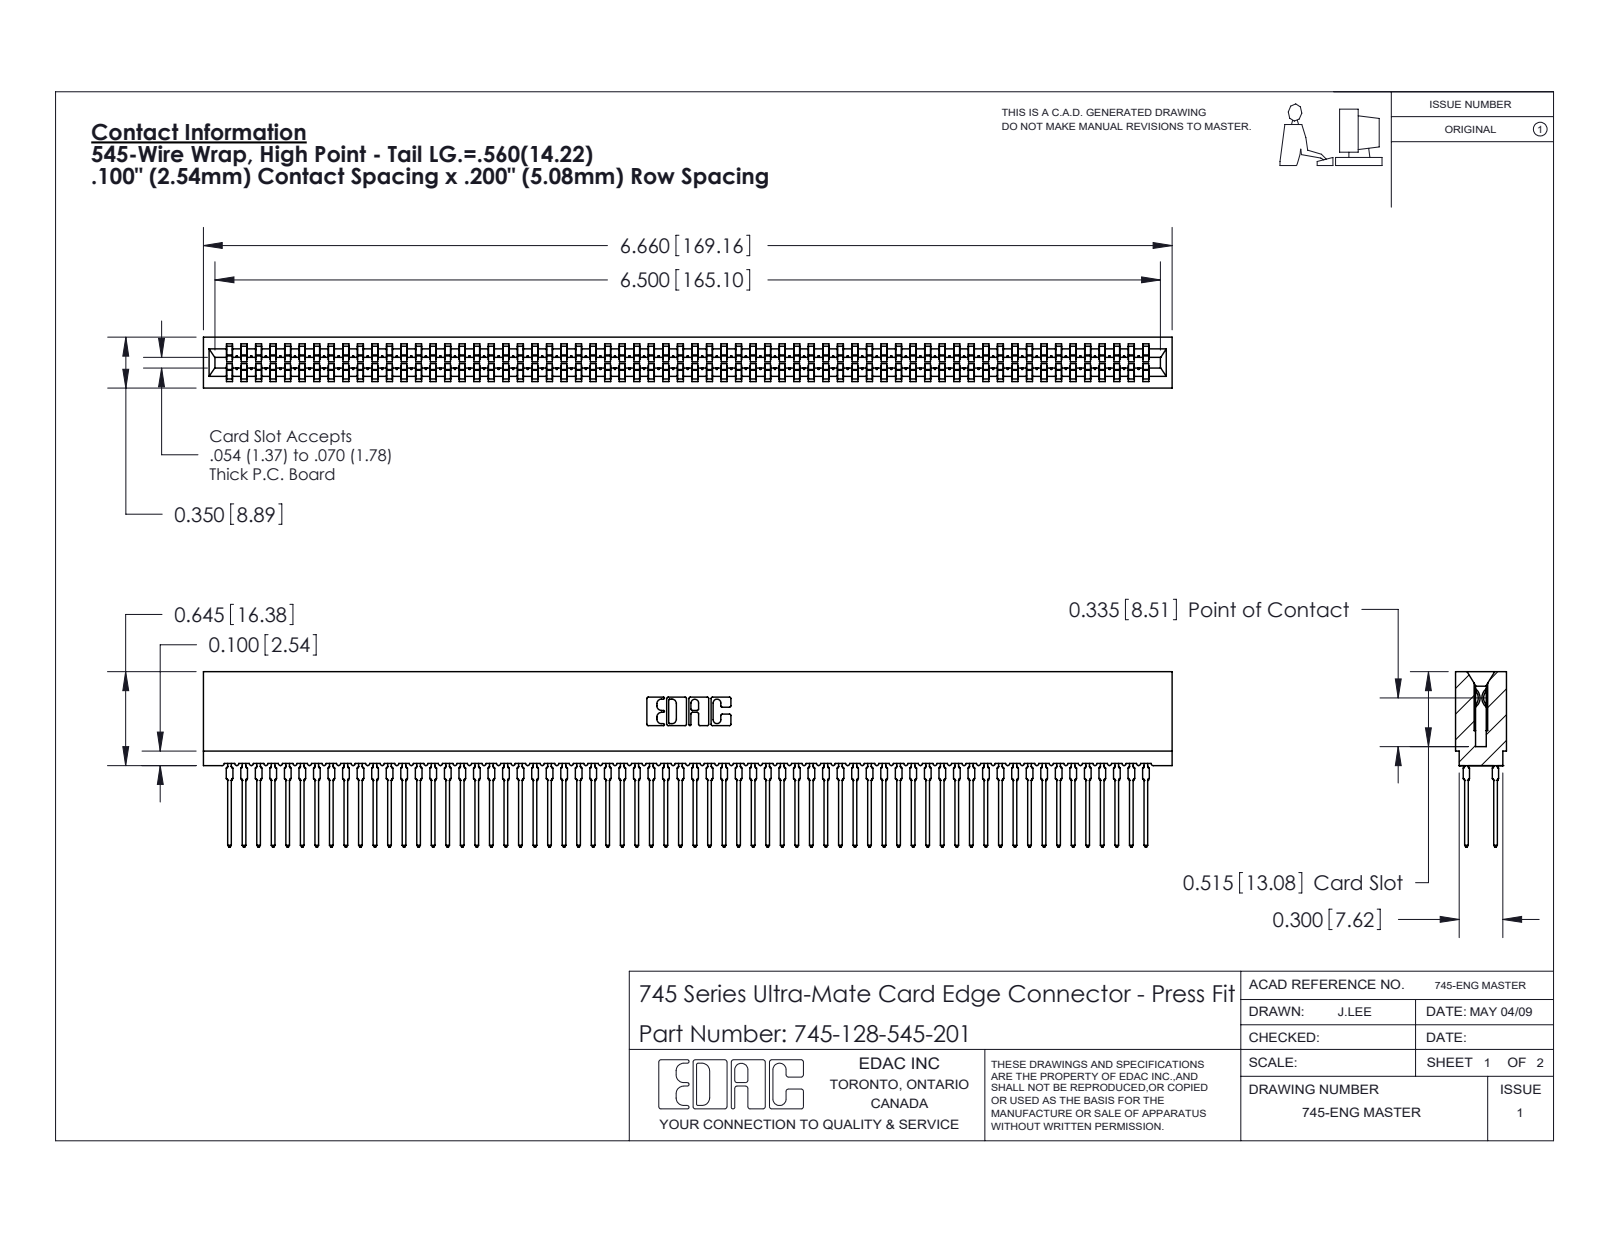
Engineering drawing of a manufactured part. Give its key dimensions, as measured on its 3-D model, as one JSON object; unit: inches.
{"part_name": "745 Part_Insulator Option - 01; 745-128-545-201; 745-292-001_545", "step_written_by": "SolidWorks 2020 (CONFIG_CONTROL_DESIGN)", "units": "inches", "bodies": {"solids": 129, "faces": 11551, "planar": 5943, "cylindrical": 2280, "other": 3328}, "overall_size": [6.66, 1.206, 0.35], "volume_in3": 0.949, "surface_area_in2": 52.82, "partial_cylinders_radius": [[0.021, 256], [0.015, 128], [0.01, 22], [0.005, 8], [0.011, 8], [0.007, 6], [0.031, 6], [0.026, 3]], "face_to_face_distances": [0.063, 0.287, 0.35, 0.045, 0.305, 0.018, 0.243, 0.138, 0.212, 0.093]}
